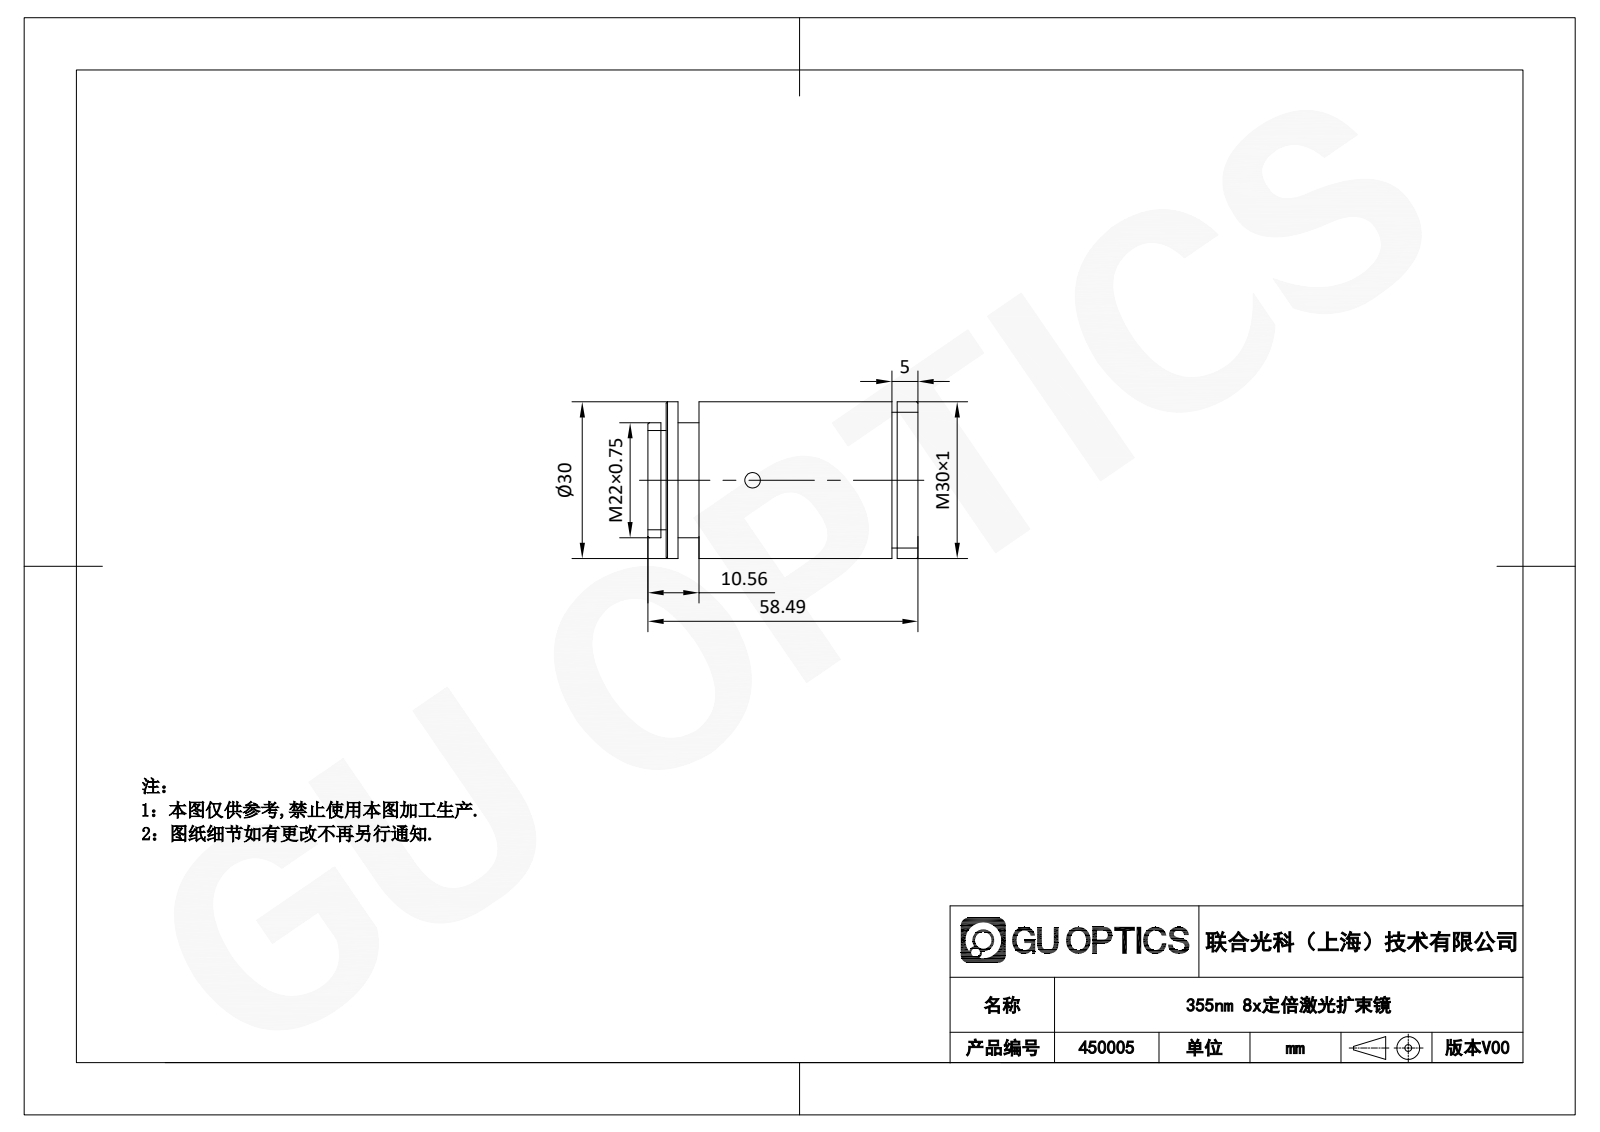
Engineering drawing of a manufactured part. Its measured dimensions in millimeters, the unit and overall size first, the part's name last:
Units: millimetres
Overall size (bounding box): 58.49 × 30 × 30
Round holes (diameter × count): ⌀8 ×1, ⌀18 ×1
Round bosses / shafts (diameter × count): ⌀30 ×1, ⌀26 ×1, ⌀22 ×1, ⌀19 ×1
Main face-to-face distances: 4, 47.93, 50.99, 54.99, 3.06, 51.93, 7.06, 43.93, 3.5, 6.56
Volume: 31 451 mm³ · Surface area: 10 510 mm²
Bodies: 1 solid, 43 faces (11 planar, 22 cylindrical, 10 other)
Part name (STEP PRODUCT): 450005
STEP written by: SolidWorks 2020 (AUTOMOTIVE_DESIGN)
